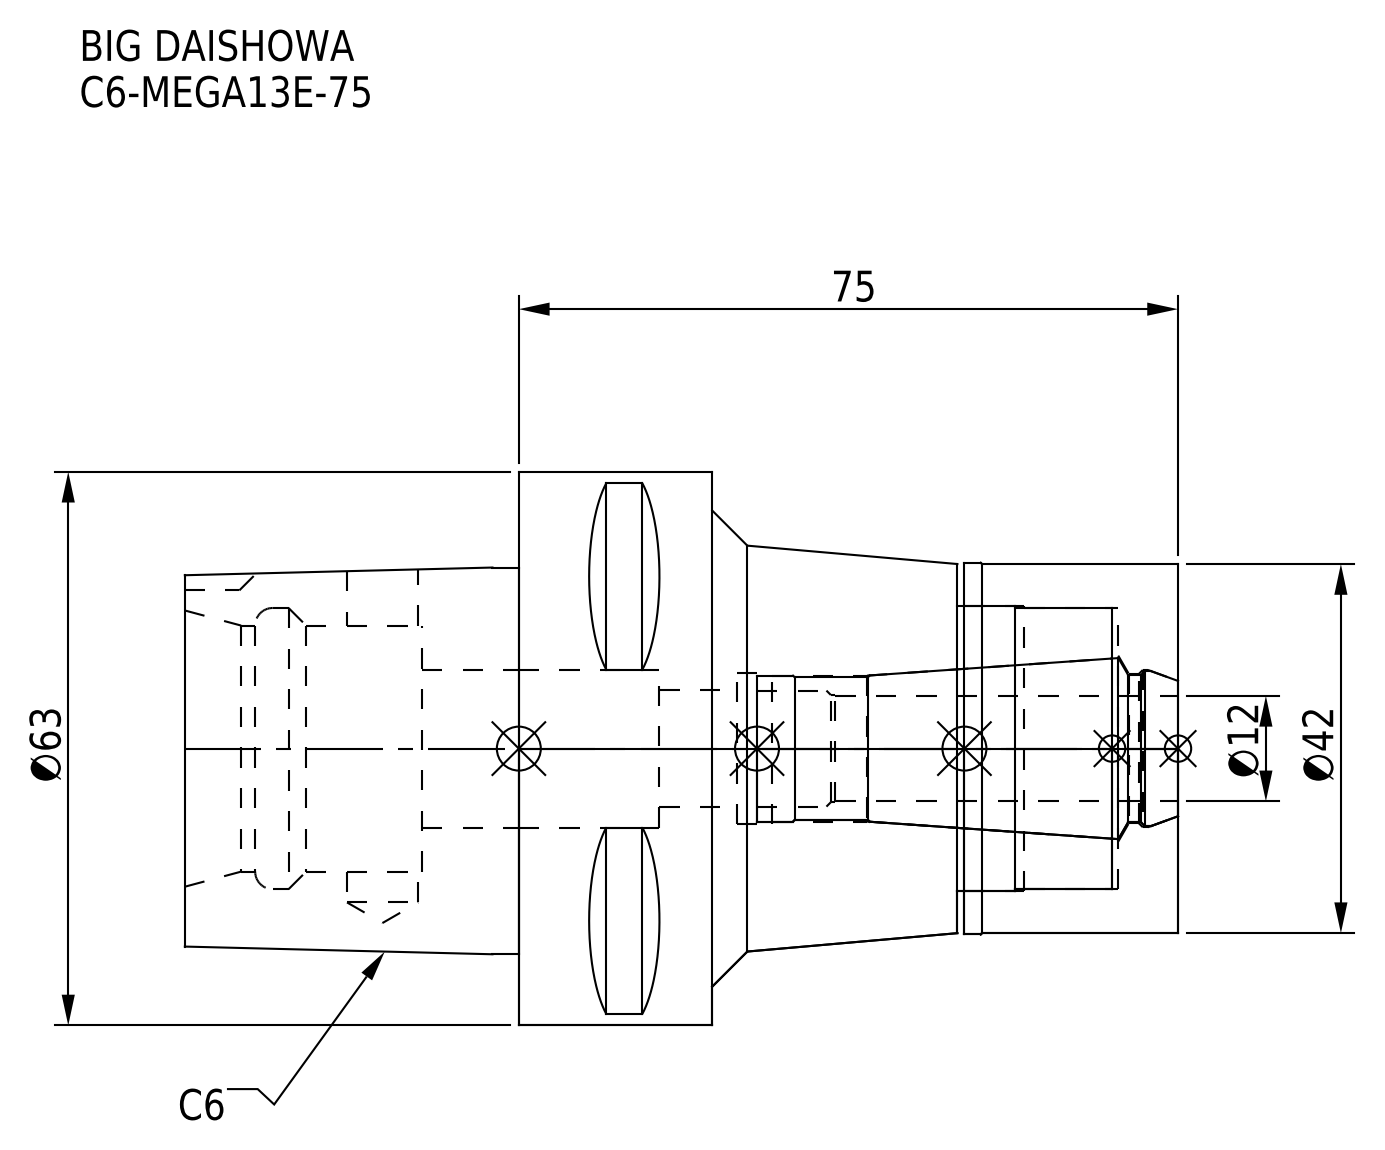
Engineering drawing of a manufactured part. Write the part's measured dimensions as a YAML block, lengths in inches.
part_name: "C6-MEGA13E-75; MEN13_1.stp; C6-MEGA13E-75-120.stp; DXF_TEMP_ASSY_ASM_4_ASM.stp (+3 more)"
step_written_by: "SolidWorks 2019 (CONFIG_CONTROL_DESIGN)"
units: inches
bodies: {solids: 2, faces: 97, planar: 36, cylindrical: 37, other: 24}
overall_size: [4.449, 2.48, 2.48]
volume: 9.833
surface_area: 54.77
round_holes:
  - {diameter: 0.319, count: 1}
  - {diameter: 0.524, count: 1}
  - {diameter: 0.654, count: 1}
  - {diameter: 0.669, count: 1}
  - {diameter: 0.677, count: 1}
  - {diameter: 0.705, count: 1}
  - {diameter: 0.709, count: 1}
  - {diameter: 1.102, count: 1}
  - {diameter: 1.26, count: 1}
  - {diameter: 1.28, count: 1}
round_bosses_or_shafts:
  - {diameter: 2.48, count: 1}
  - {diameter: 1.665, count: 1}
  - {diameter: 1.654, count: 1}
partial_cylinders:
  - {radius: 0.197, count: 1}
face_to_face_distances: [2.953, 2.087, 0.866, 0.988, 1.13, 0.957, 1.996, 0.031, 1.098, 1.965]
